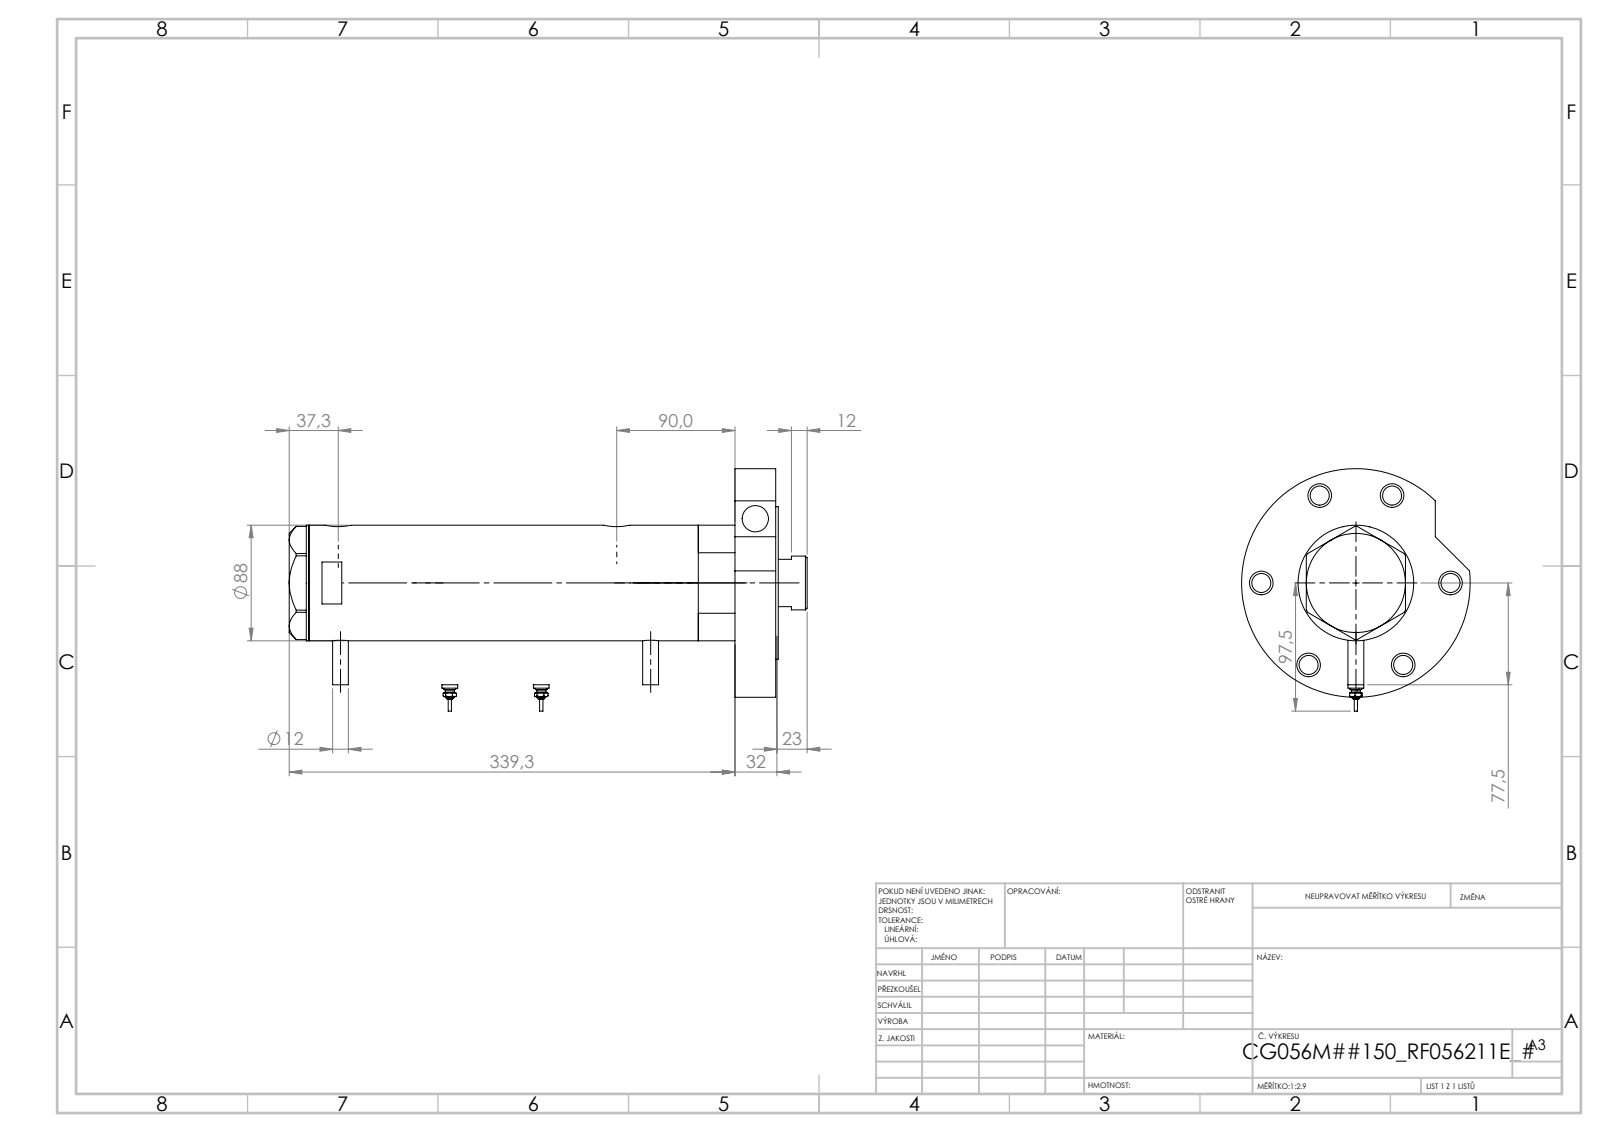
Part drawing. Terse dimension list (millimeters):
name: V270CG_FRONT; V270CG_MIDDLE; V270CG_SWITCH; V270CG_VC (+2 more)
written by: SolidWorks 2019 (CONFIG_CONTROL_DESIGN)
unit: mm
bodies: 7 solids, 276 faces (92 planar, 110 cylindrical, 74 other)
size: 374.47 × 174 × 174
volume: 2 435 000 mm³; area: 347 526 mm²
holes: 7× ⌀14.5, 6× ⌀18, 3× ⌀20, 2× ⌀5, 2× ⌀12.5, 2× ⌀13.16, 1× ⌀42, 1× ⌀43.5, 1× ⌀56, 1× ⌀60, 1× ⌀75, 1× ⌀80
bosses: 2× ⌀12, 2× ⌀9, 2× ⌀7, 2× ⌀4.34, 2× ⌀2.4, 1× ⌀174, 1× ⌀116, 1× ⌀88
face distances: 31, 2, 334.9, 301.9, 332.9, 33, 224.4, 77.5, 108.5, 110.5
hole spacings: 72, 80, 119.73, 124.71, 129.15, 143.69, 1.7, 25.8
